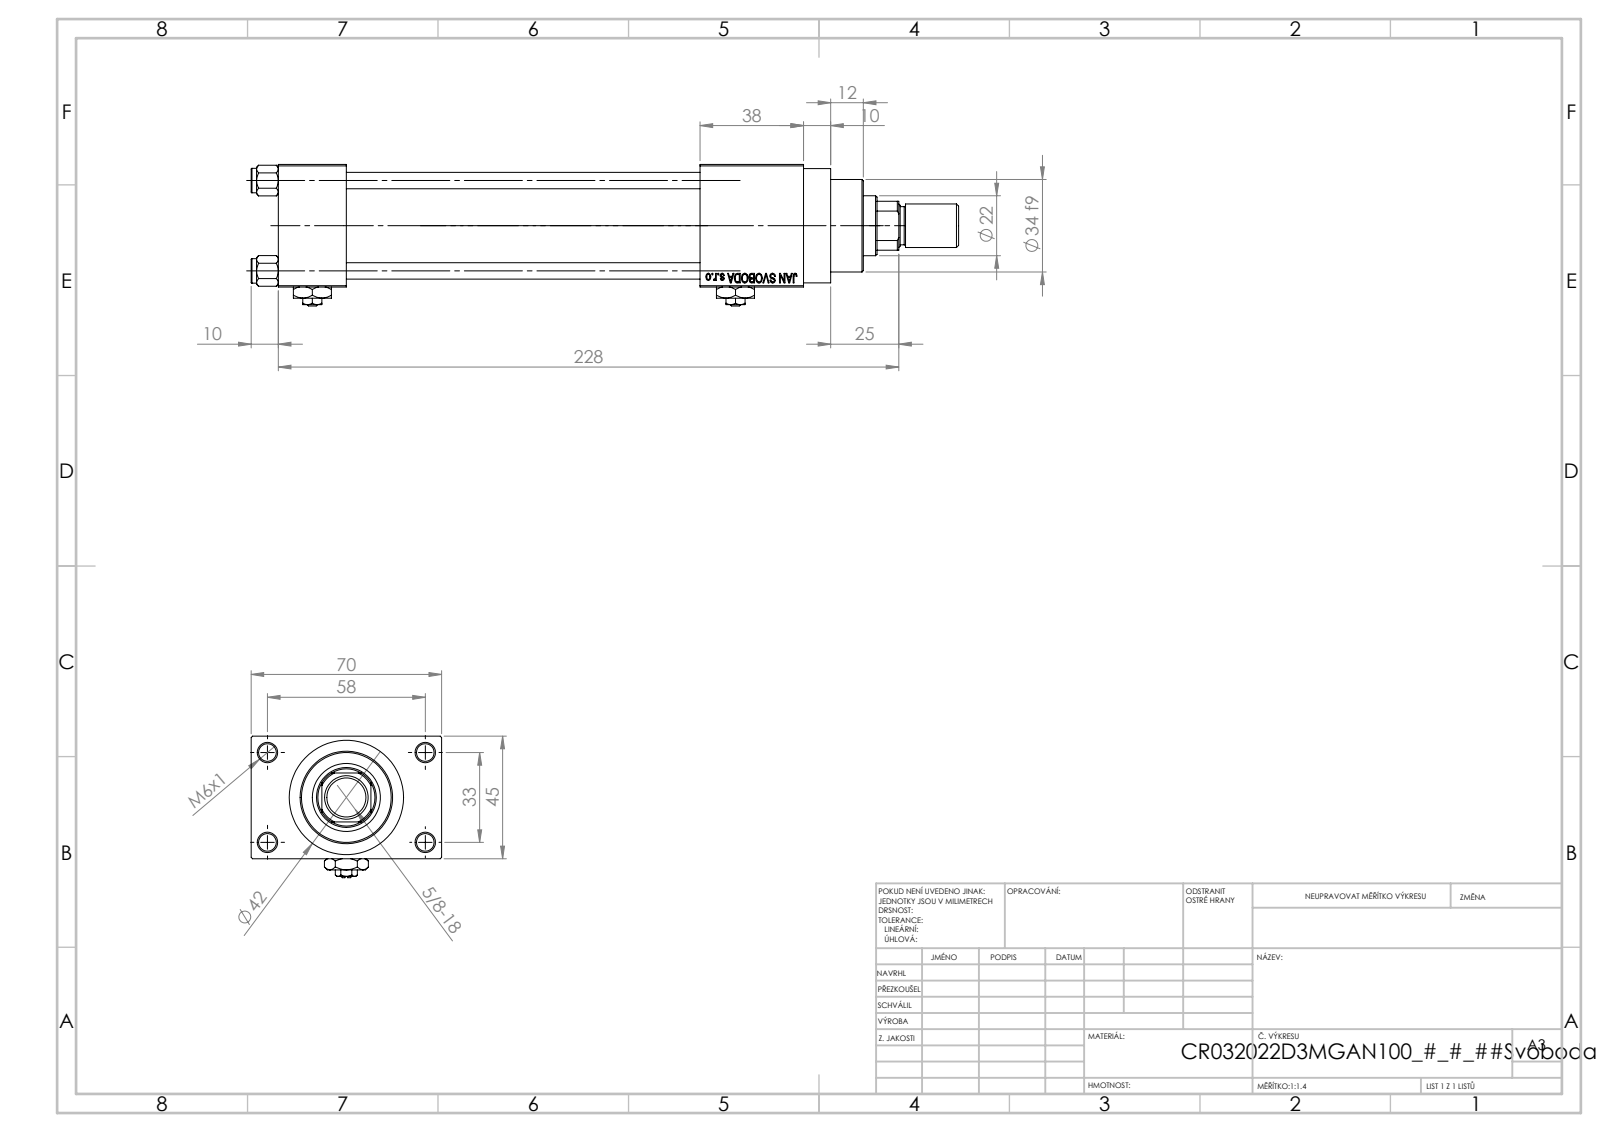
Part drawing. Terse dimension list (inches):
name: V215CR_D_Body; V215CR_VCP_D; V215CR_D_TYCINKA; NUT_M5_D (+3 more)
written by: SolidWorks 2019 (CONFIG_CONTROL_DESIGN)
unit: in
bodies: 14 solids, 1216 faces (546 planar, 104 cylindrical, 566 other)
size: 10.236 × 2.756 × 2.047
volume: 19.13 in³; area: 173.4 in²
holes: 4× ⌀0.236, 4× ⌀0.256, 2× ⌀0.276, 2× ⌀0.518, 2× ⌀0.787, 1× ⌀0.413, 1× ⌀0.866, 1× ⌀0.945, 1× ⌀0.984, 1× ⌀1.26, 1× ⌀1.299
bosses: 4× ⌀0.354, 1× ⌀1.654, 1× ⌀1.496, 1× ⌀1.339, 1× ⌀0.63, 1× ⌀0.551
rounds: 1× R0.413
face distances: 1.772, 0.984, 0.492, 2.264, 5.118, 6.102, 6.614, 1.496, 2.756, 7.598
hole spacings: 0.488, 0.924, 1.307, 1.314, 1.392, 1.795, 2.219, 1.299
